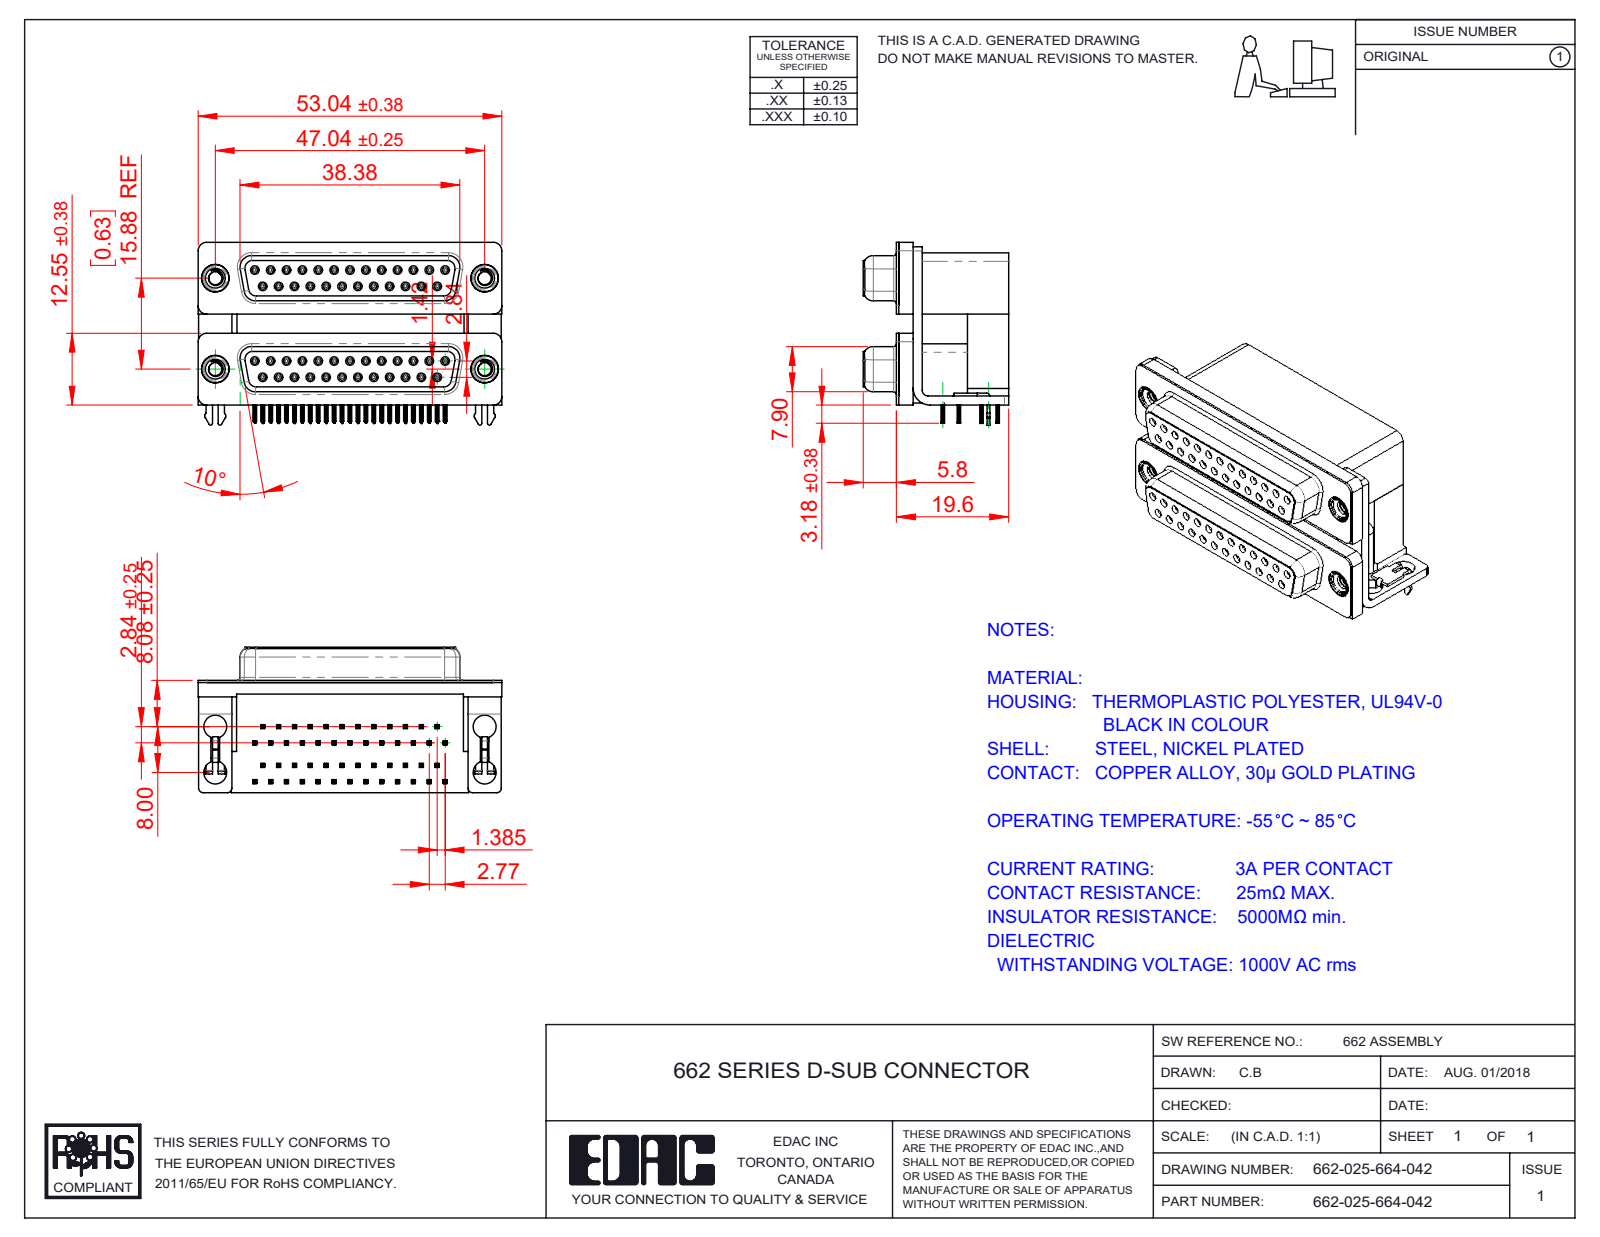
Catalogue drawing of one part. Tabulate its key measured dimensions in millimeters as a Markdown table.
| quantity | value |
| --- | --- |
| part name | 662 Contact Bottom Upper_L; 662 Contact Top Upper_L; 662 Threaded Rivet_4-40; 662 Contact Top Lower (+8 more) |
| STEP written by | SolidWorks 2020 (CONFIG_CONTROL_DESIGN) |
| units | millimeters |
| bodies | 63 solids, 7900 faces (3654 planar, 1834 cylindrical, 2412 other) |
| overall size | 53.04 × 31.93 × 25.4 |
| volume | 22 891 mm³ |
| surface area | 25 144 mm² |
| round holes (diameter × count) | 0.8 × 50, 0.9 × 50, 4 × 8, 2.26 × 4, 3.5 × 4, 4.8 × 4, 5 × 4 |
| round bosses / shafts (diameter × count) | 1.2 × 50, 4.9 × 4, 4.75 × 4, 3.9 × 4 |
| partial cylindrical surfaces (radius × count) | 0.1 × 401, 0.15 × 200, 0.35 × 100, 0.34 × 50, 0.28 × 24, 1.35 × 18, 1.5 × 13, 0.5 × 12 |
| main face-to-face distances | 15.88, 19.2, 0.4, 7.2, 12, 10.7, 6.2, 16.7, 9.5, 2.5 |
| hole center spacings | 3.16, 2.77, 5.54, 11.08, 8.31, 5.03, 13.85, 7.48 |
